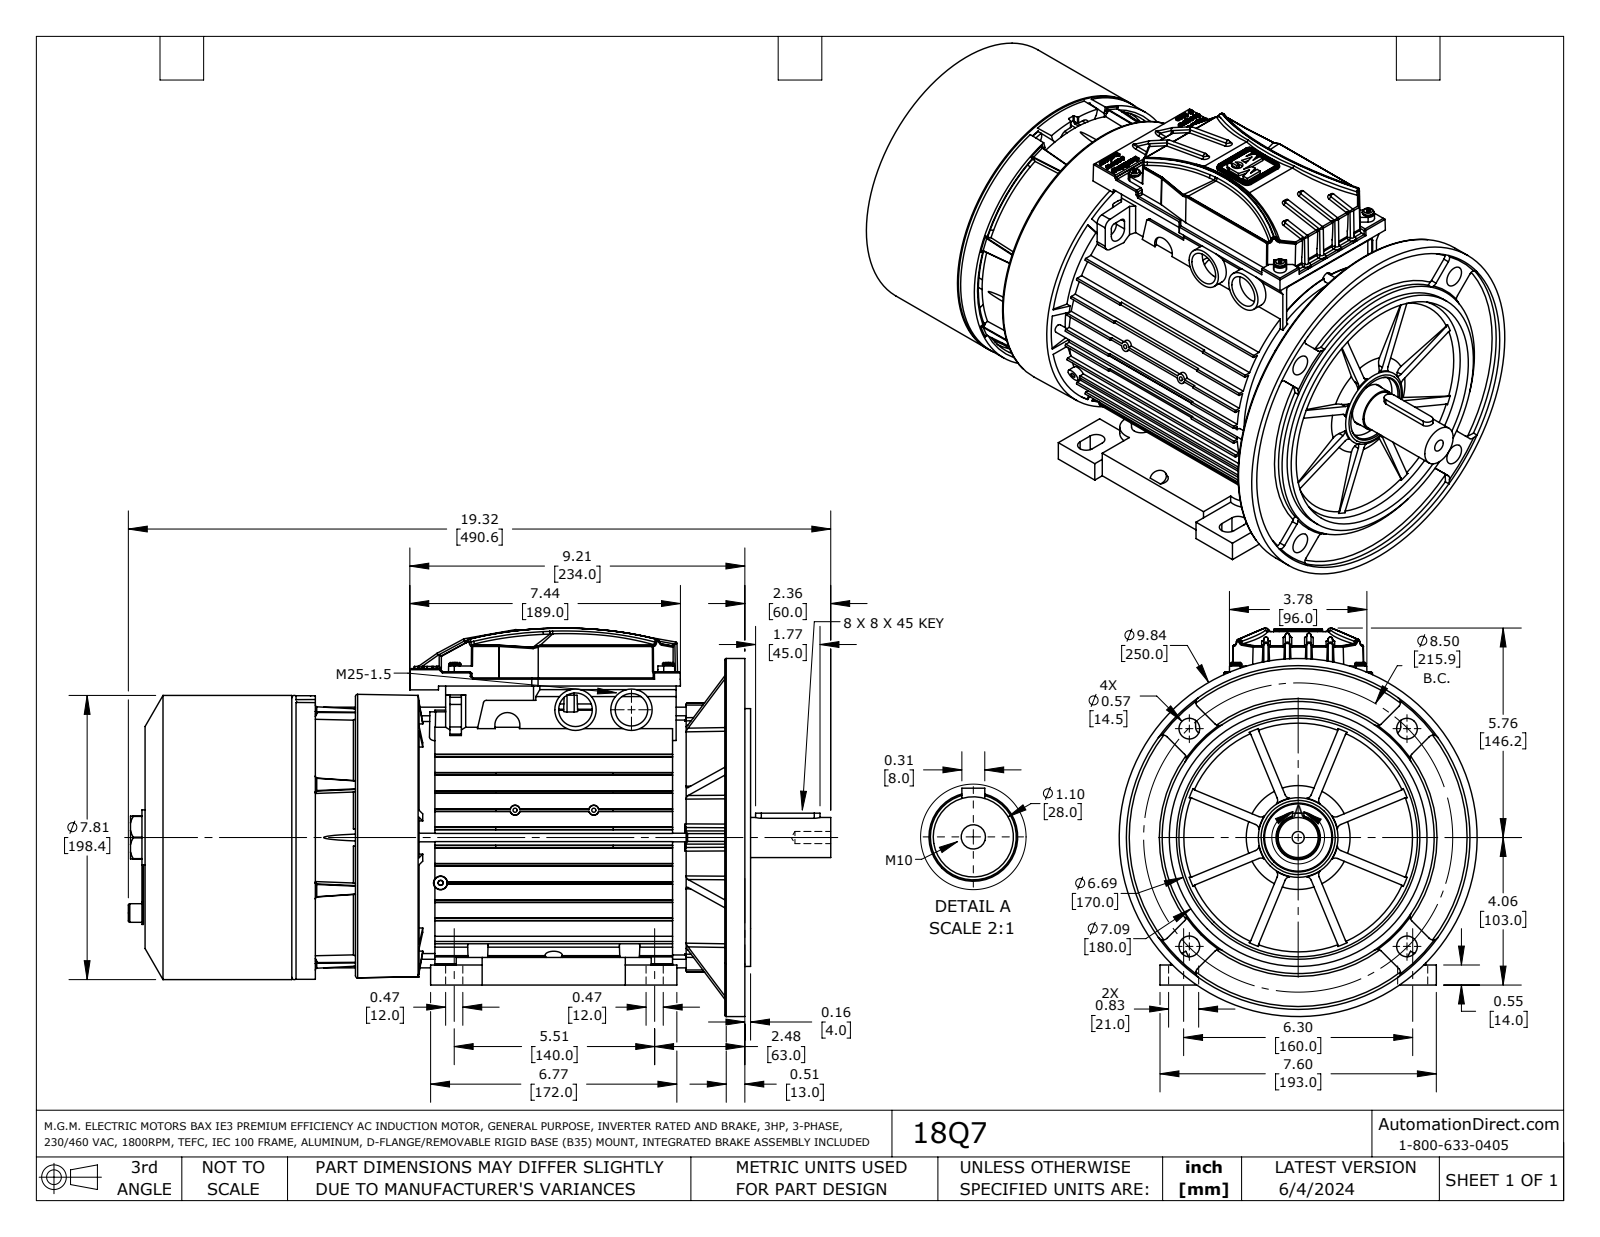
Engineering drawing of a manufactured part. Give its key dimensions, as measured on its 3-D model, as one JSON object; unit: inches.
{"part_name": "18Q7", "step_written_by": "SolidWorks 2021 (AUTOMOTIVE_DESIGN)", "units": "inches", "bodies": {"solids": 11, "faces": 3680, "planar": 1444, "cylindrical": 996, "other": 1240}, "overall_size": [19.316, 10.679, 9.843], "volume_in3": 651.4, "surface_area_in2": 1444, "round_holes": [[0.13, 14], [0.098, 5], [0.335, 5], [0.15, 4], [0.177, 4], [0.197, 4], [0.531, 4], [0.571, 4], [0.118, 2], [0.315, 1], [0.472, 1], [0.512, 1]], "round_bosses_or_shafts": [[0.315, 8], [0.138, 6], [0.522, 4], [0.236, 4], [0.276, 3], [1.138, 2], [9.843, 1], [7.811, 1]], "partial_cylinders_radius": [[0.157, 101], [0.008, 56], [0.059, 49], [0.079, 25], [0.004, 24], [0.039, 24], [0.02, 22], [0.031, 20]], "face_to_face_distances": [0.039, 1.673, 1.102, 1.634, 1.142, 0.531, 1.319, 5.825, 5.785, 4.683], "hole_center_spacings": [0.472, 3.024, 7.081, 0.818, 3.425, 3.025, 3.215, 3.457]}
